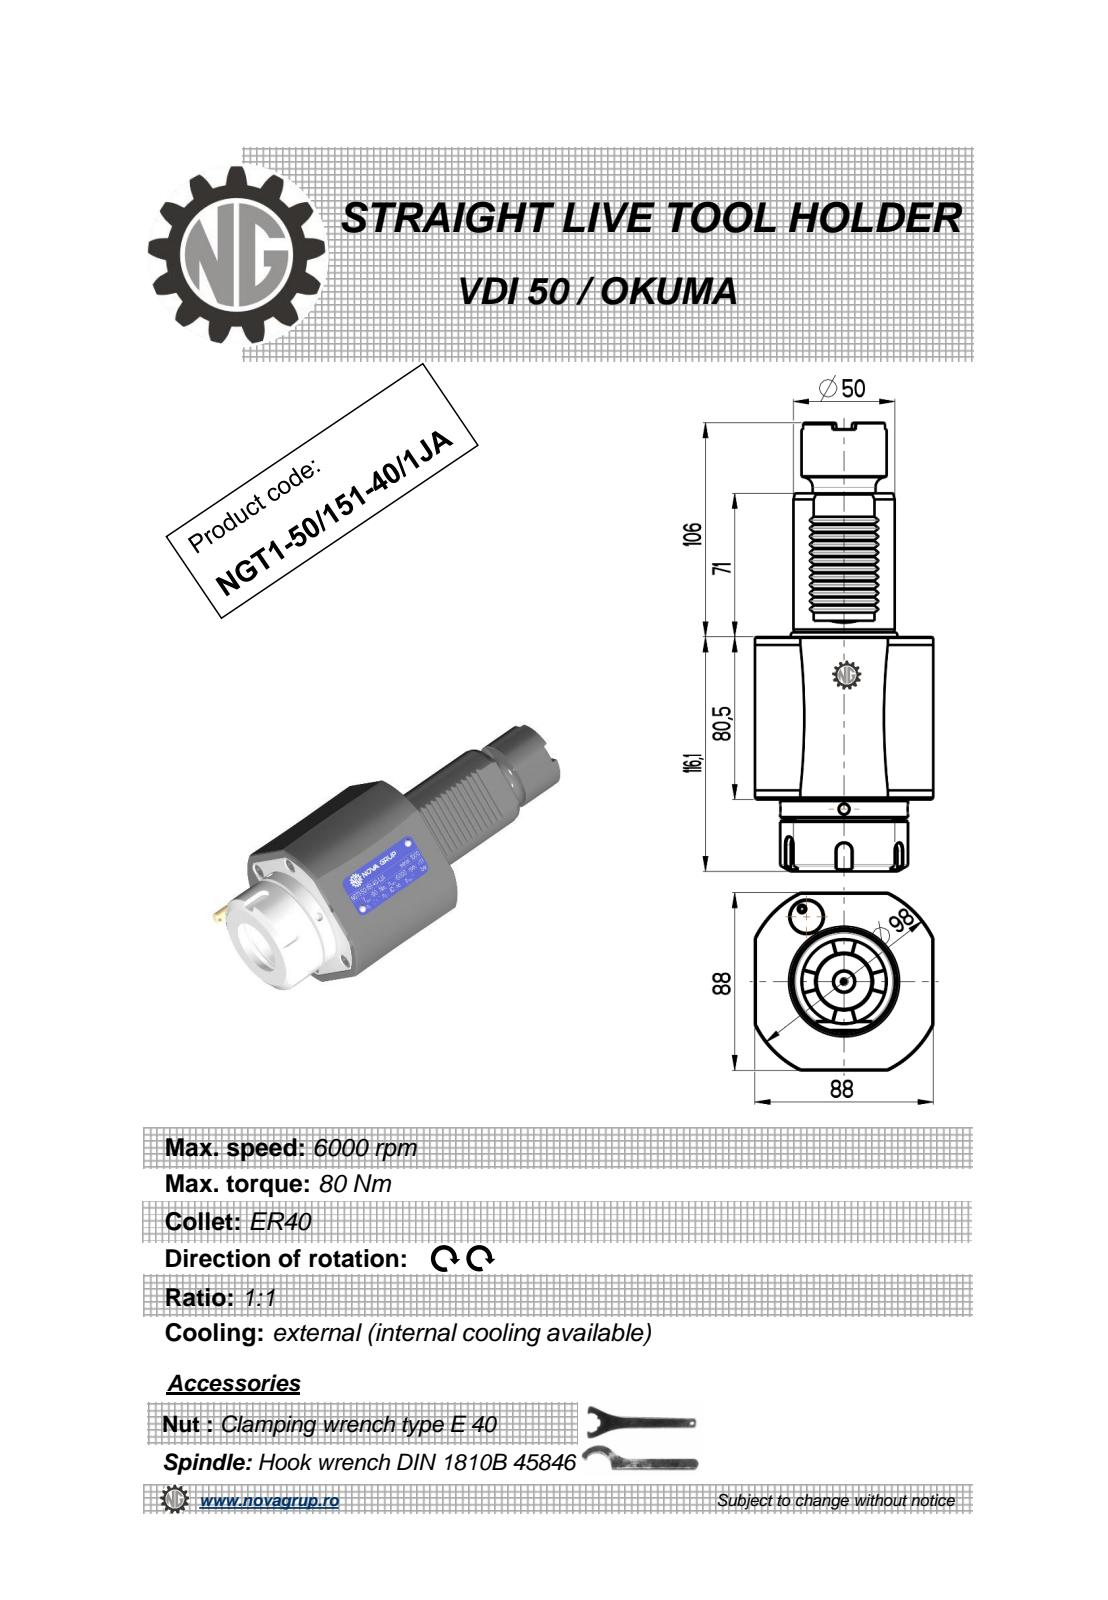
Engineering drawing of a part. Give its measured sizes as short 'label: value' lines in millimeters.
name: NGT1_50_141_40_1JA
written by: PRO/ENGINEER BY PARAMETRIC TECHNOLOGY CORPORATION, 2010280 (CONFIG_CONTROL_DESIGN)
unit: mm
bodies: 1 solid, 317 faces (124 planar, 63 cylindrical, 130 other)
size: 222.1 × 89.6 × 88
volume: 826 861 mm³; area: 68 984 mm²
holes: 2× ⌀5, 1× ⌀2.5, 1× ⌀3, 1× ⌀28
bosses: 1× ⌀63, 1× ⌀51, 1× ⌀50, 1× ⌀42, 1× ⌀31, 1× ⌀9, 1× ⌀7, 1× ⌀5
rounds: 12× R0.3, 5× R3.75, 1× R49
face distances: 88, 80.5, 116.1, 35.6, 109.9, 29.4, 6.2, 0.5, 2.83, 9
hole spacings: 41.5
